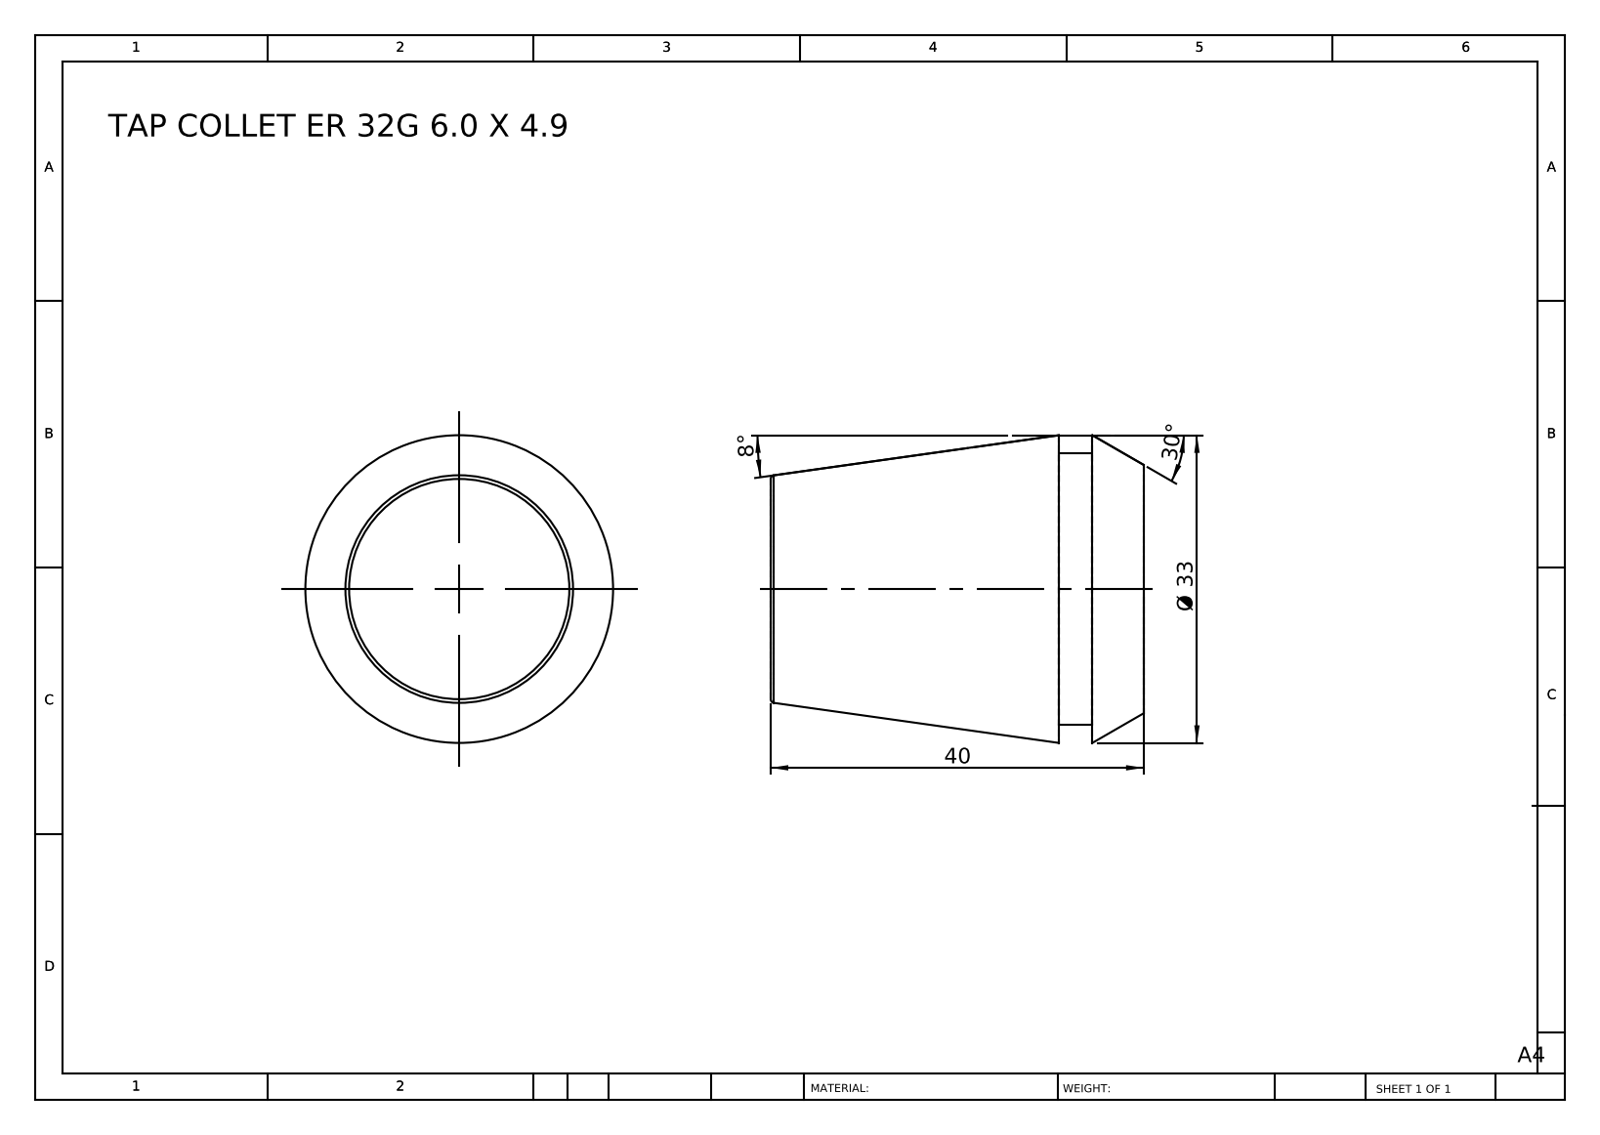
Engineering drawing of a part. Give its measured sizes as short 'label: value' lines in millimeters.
name: TAP COLLET ER 32G 6.0 X 4.9
written by: SolidWorks 2014 (CONFIG_CONTROL_DESIGN)
unit: mm
bodies: 1 solid, 12 faces (4 planar, 2 cylindrical, 6 other)
size: 40 × 33 × 33
volume: 26 350 mm³; area: 5 119 mm²
bosses: 1× ⌀29.2
face distances: 40, 9.1, 30.9, 5.5, 3.6, 34.5
